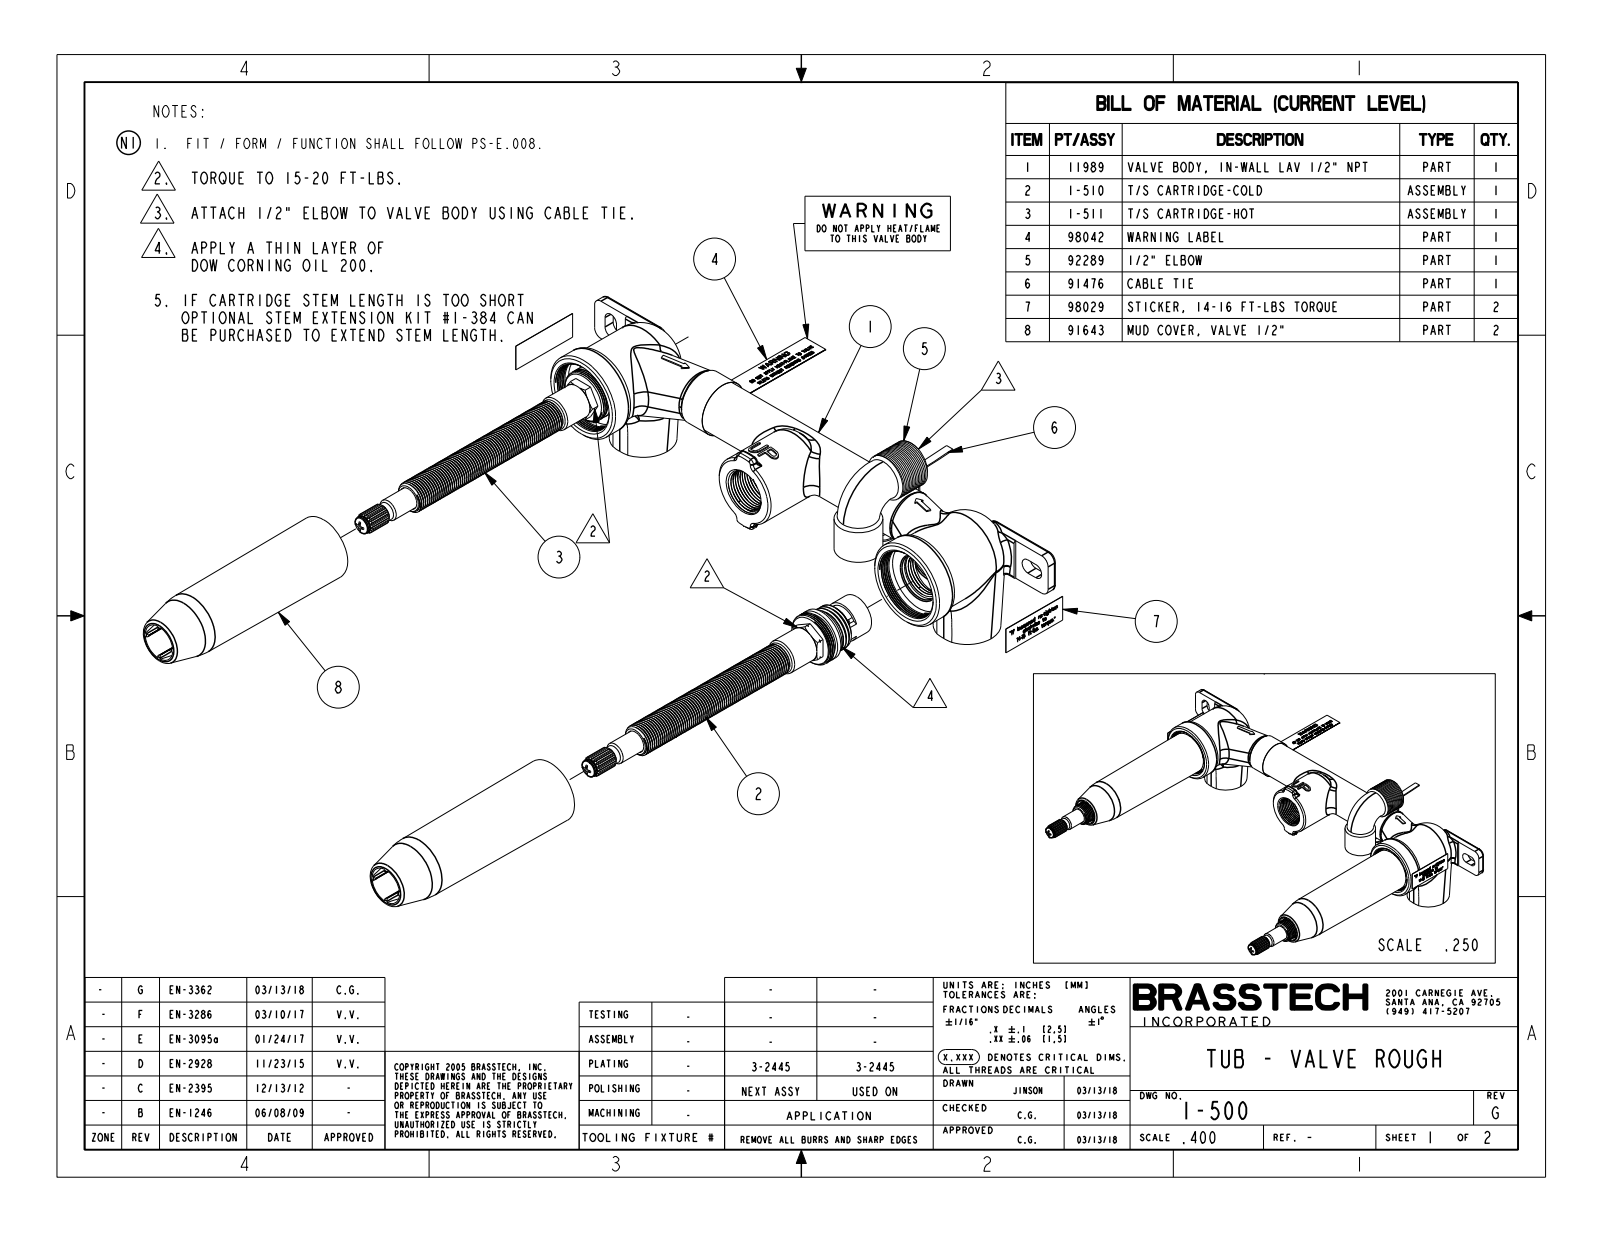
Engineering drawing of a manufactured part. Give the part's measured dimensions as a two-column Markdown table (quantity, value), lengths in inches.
| quantity | value |
| --- | --- |
| part name | 11989; 1-147; 10489; 12062 (+8 more) |
| STEP written by | PRO/ENGINEER BY PARAMETRIC TECHNOLOGY CORPORATION, 2013150 (CONFIG_CONTROL_DESIGN) |
| units | inches |
| bodies | 14 solids, 9476 faces (6377 planar, 1949 cylindrical, 1150 other) |
| overall size | 11.024 × 9.45 × 2.82 |
| volume | 10.65 in³ |
| surface area | 311.6 in² |
| round holes (diameter × count) | 0.748 × 5, 0.13 × 2, 0.165 × 2, 0.172 × 2, 0.33 × 2, 0.394 × 2, 0.406 × 2, 0.44 × 2, 0.516 × 2, 0.57 × 2, 0.633 × 2, 0.669 × 2 |
| round bosses / shafts (diameter × count) | 0.029 × 4, 1.575 × 2, 1.417 × 2, 0.945 × 2, 0.84 × 2, 0.832 × 2, 0.823 × 2, 0.728 × 2 |
| partial cylindrical surfaces (radius × count) | 0.039 × 11, 0.04 × 10, 0.079 × 8, 0.08 × 8, 0.079 × 6, 0.157 × 6, 0.197 × 3, 0.039 × 2 |
| main face-to-face distances | 0.197, 0.945, 0.748, 0.315, 2.087, 0.185, 1.181, 1.142, 0.906, 0.157 |
| hole center spacings | 3.937, 7.874, 1.878, 1.939, 2.396, 6.242, 6.26 |
